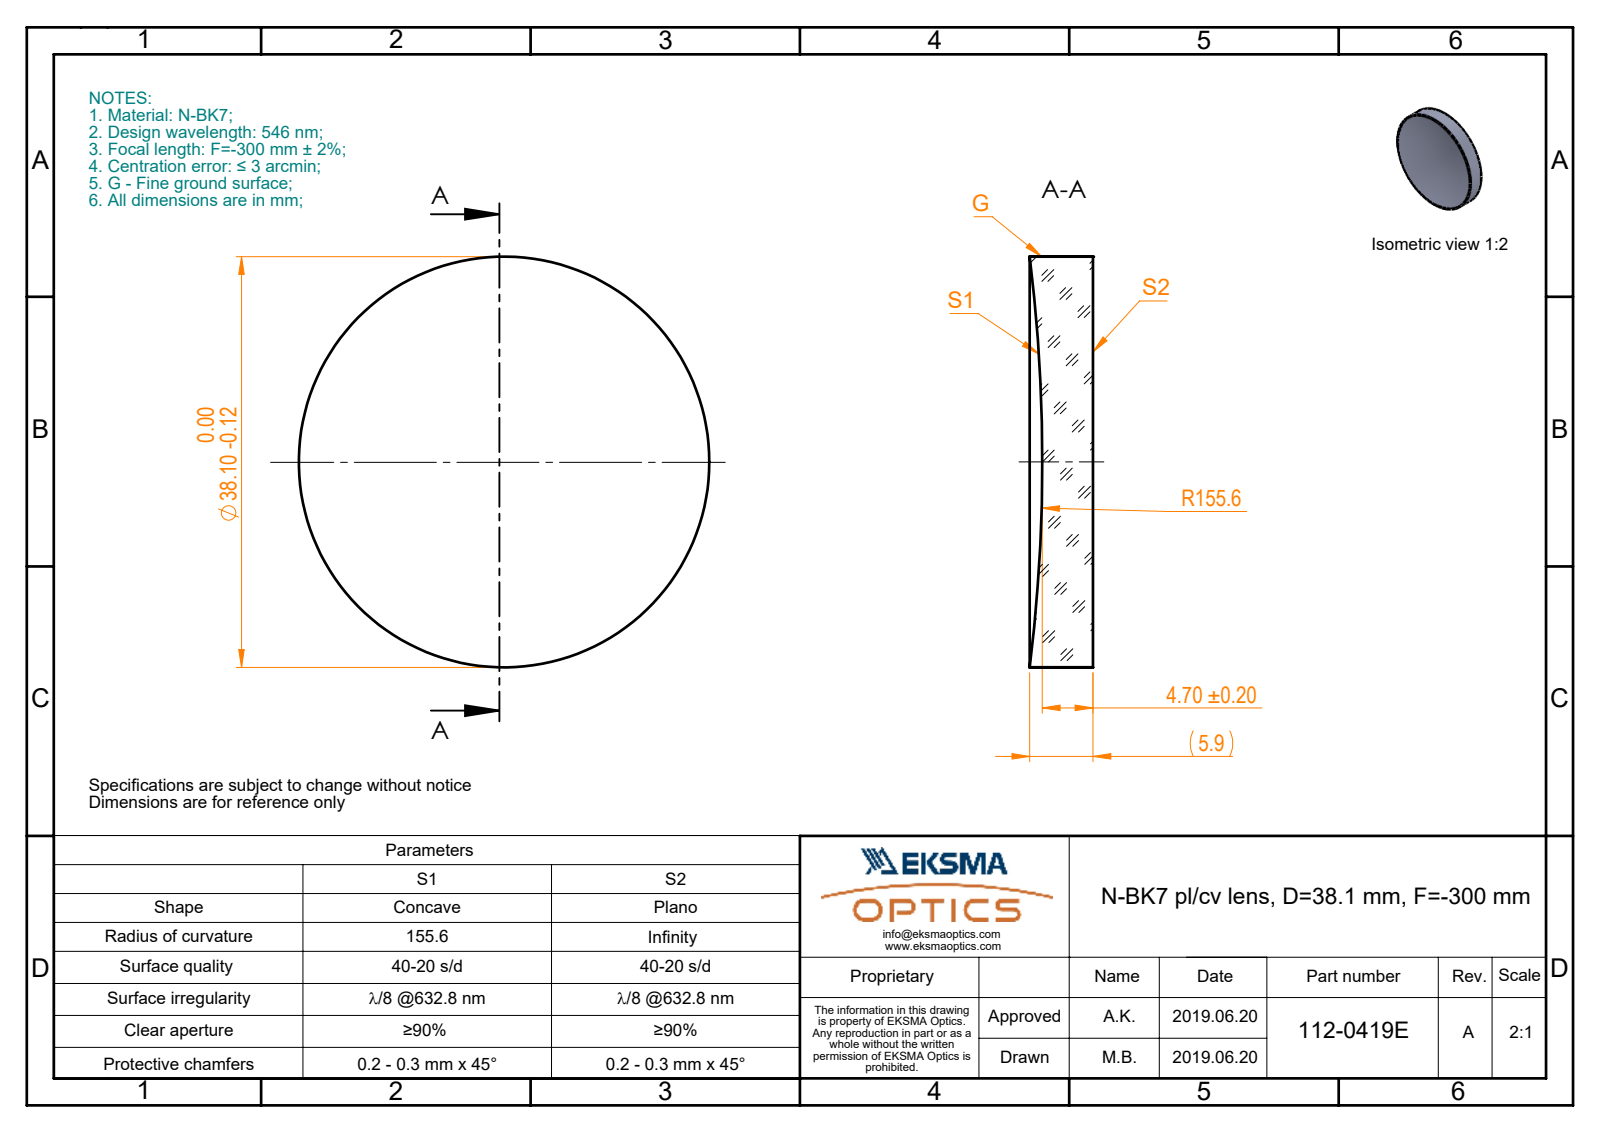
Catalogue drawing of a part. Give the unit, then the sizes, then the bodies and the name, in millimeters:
Units: millimetres
Overall size (bounding box): 38.1 × 38.1 × 5.87
Round bosses / shafts (diameter × count): ⌀38.1 ×1
Volume: 6 025 mm³ · Surface area: 2 987 mm²
Bodies: 1 solid, 5 faces (1 planar, 2 cylindrical, 2 other)
Part name (STEP PRODUCT): 112-0419E BK7 pl-cv 38.1 F-300
STEP written by: SolidWorks 2017 (CONFIG_CONTROL_DESIGN)
